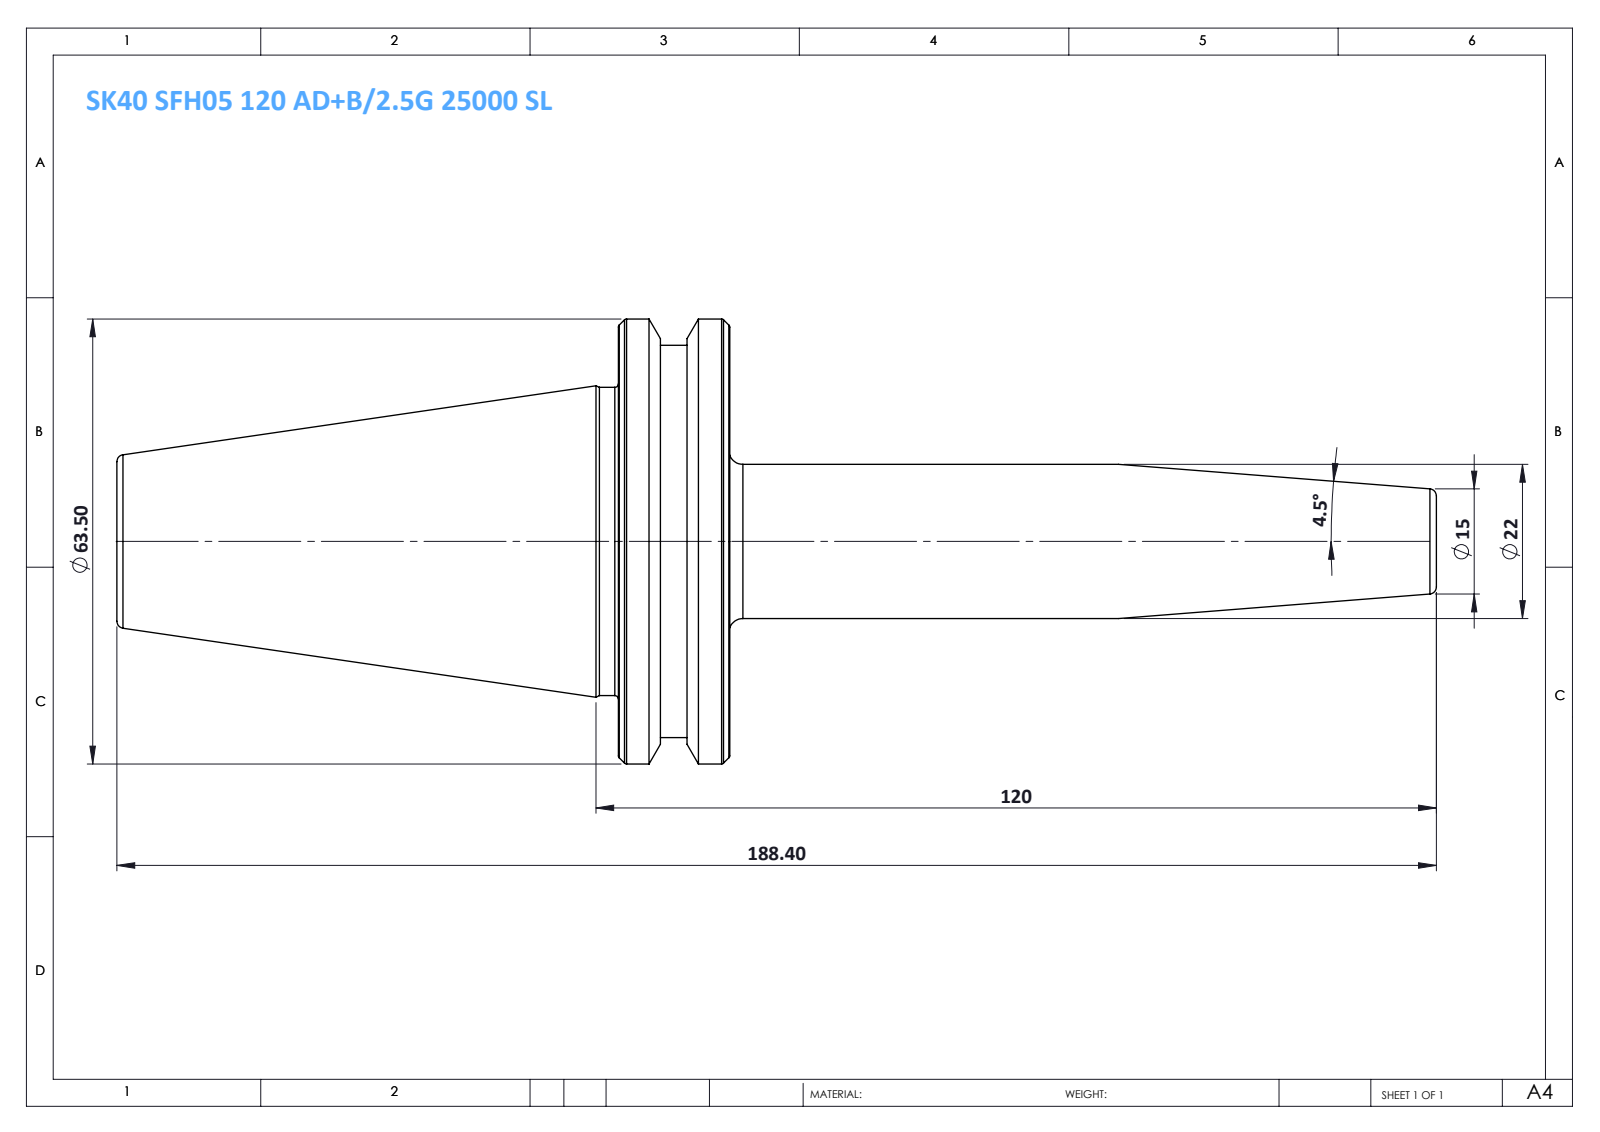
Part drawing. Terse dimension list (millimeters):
name: SK40 SFH05 120 AD+B-2.5G 25000 SL
written by: SolidWorks 2014 (CONFIG_CONTROL_DESIGN)
unit: mm
bodies: 1 solid, 46 faces (6 planar, 10 cylindrical, 30 other)
size: 188.4 × 63.5 × 63.5
volume: 150 495 mm³; area: 23 125 mm²
bosses: 1× ⌀63.5, 1× ⌀56, 1× ⌀44, 1× ⌀22
face distances: 15.9, 87.5, 71.6, 6.1, 9.8, 81.4, 9.9, 3.8, 6, 77.6
